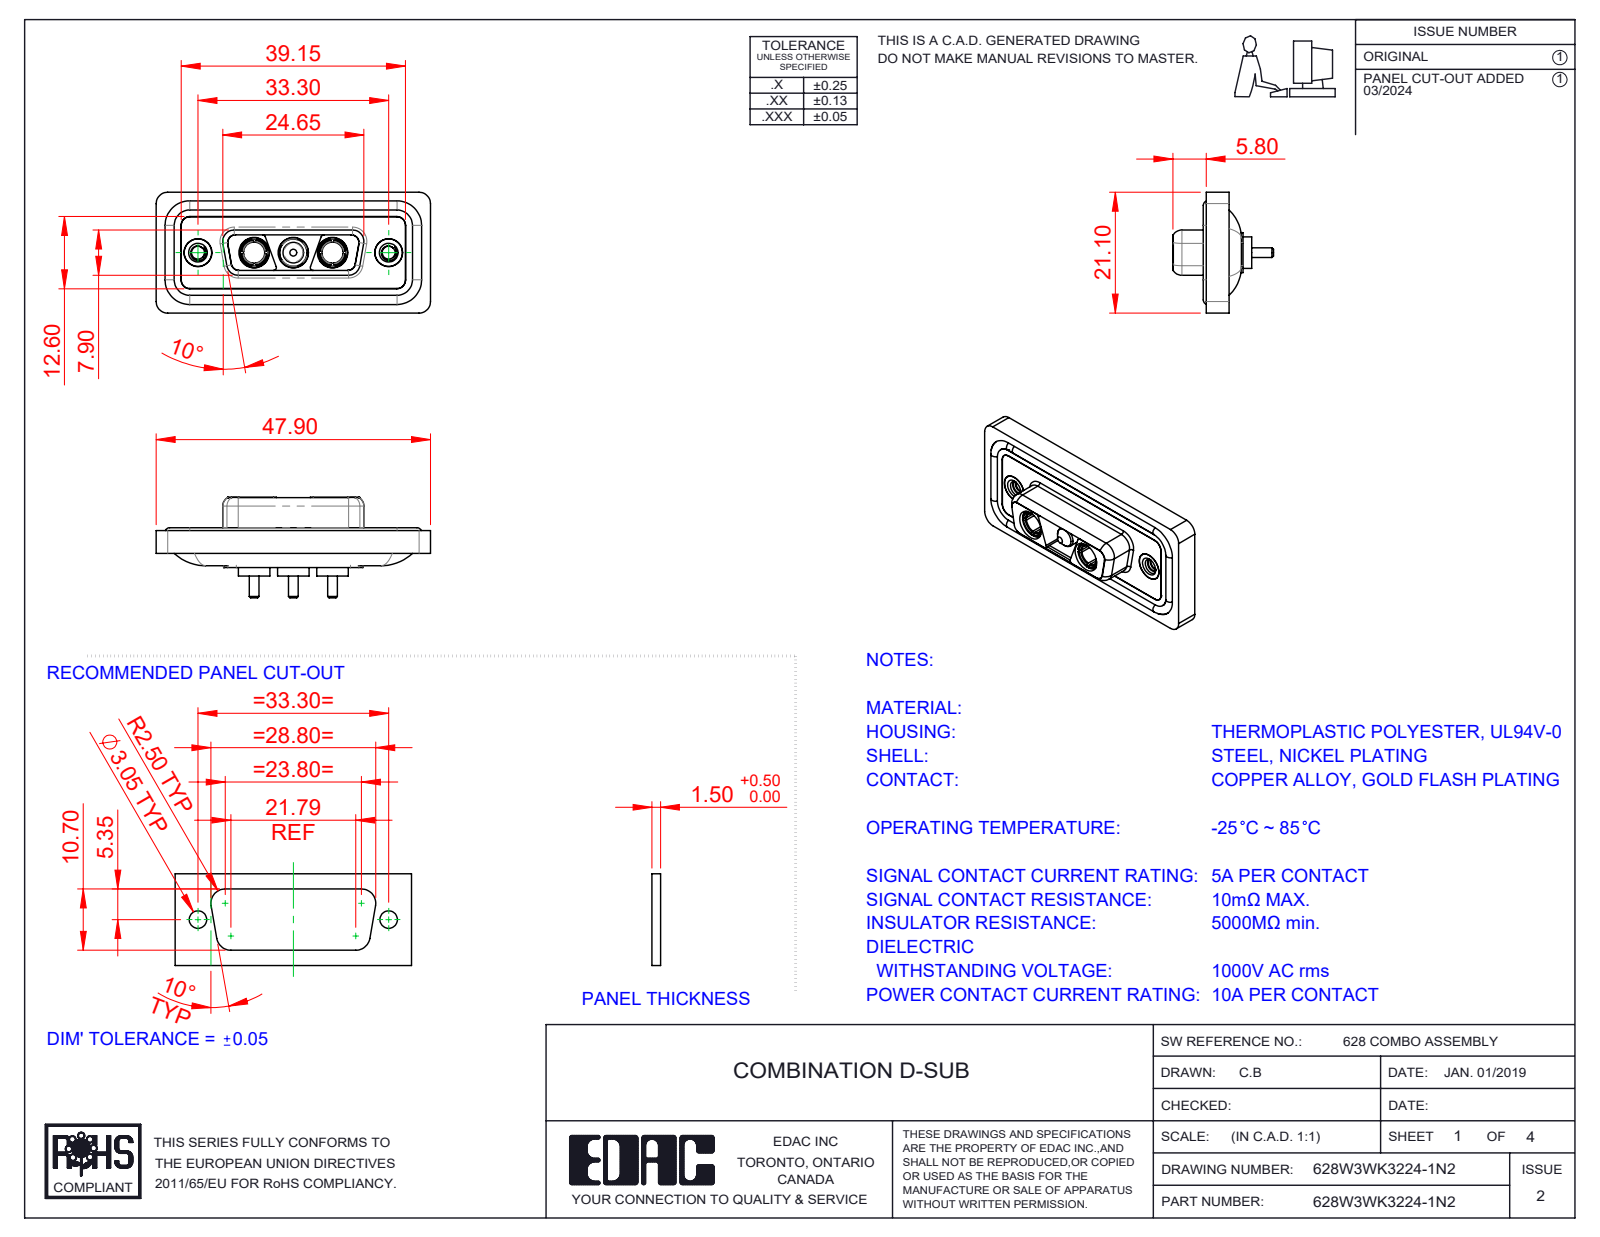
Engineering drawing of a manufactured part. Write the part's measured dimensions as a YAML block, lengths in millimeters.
part_name: "628Combo Shell Front_15 Contacts; 628Combo Waterproof Housing_15 Contacts; 628Combo Threaded Rivet_2; 628Combo Shell Rear_15 Contacts (+4 more)"
step_written_by: "SolidWorks 2023 (CONFIG_CONTROL_DESIGN)"
units: millimeters
bodies: {solids: 13, faces: 583, planar: 178, cylindrical: 258, other: 147}
overall_size: [47.9, 21.1, 17.55]
volume: 5834
surface_area: 9467
round_holes:
  - {diameter: 4.85, count: 5}
  - {diameter: 5.3, count: 3}
  - {diameter: 2.26, count: 2}
  - {diameter: 3.7, count: 2}
  - {diameter: 4, count: 2}
  - {diameter: 4.05, count: 2}
  - {diameter: 5, count: 2}
round_bosses_or_shafts:
  - {diameter: 1.6, count: 4}
  - {diameter: 5.5, count: 3}
  - {diameter: 5.2, count: 3}
  - {diameter: 4.75, count: 3}
  - {diameter: 3.75, count: 3}
  - {diameter: 1.7, count: 3}
  - {diameter: 4.96, count: 2}
  - {diameter: 4.95, count: 2}
partial_cylinders:
  - {radius: 1.5, count: 22}
  - {radius: 2, count: 20}
  - {radius: 1.35, count: 12}
  - {radius: 0.5, count: 8}
  - {radius: 1.6, count: 8}
  - {radius: 0.25, count: 4}
  - {radius: 0.6, count: 4}
  - {radius: 0.65, count: 4}
face_to_face_distances: [0.4, 1.6, 1.8, 0.5, 1.1, 2.9, 5.65, 7.05, 1.5, 5.35]
hole_center_spacings: [6.85, 9.8, 16.65, 23.5, 13.7, 33.3]
